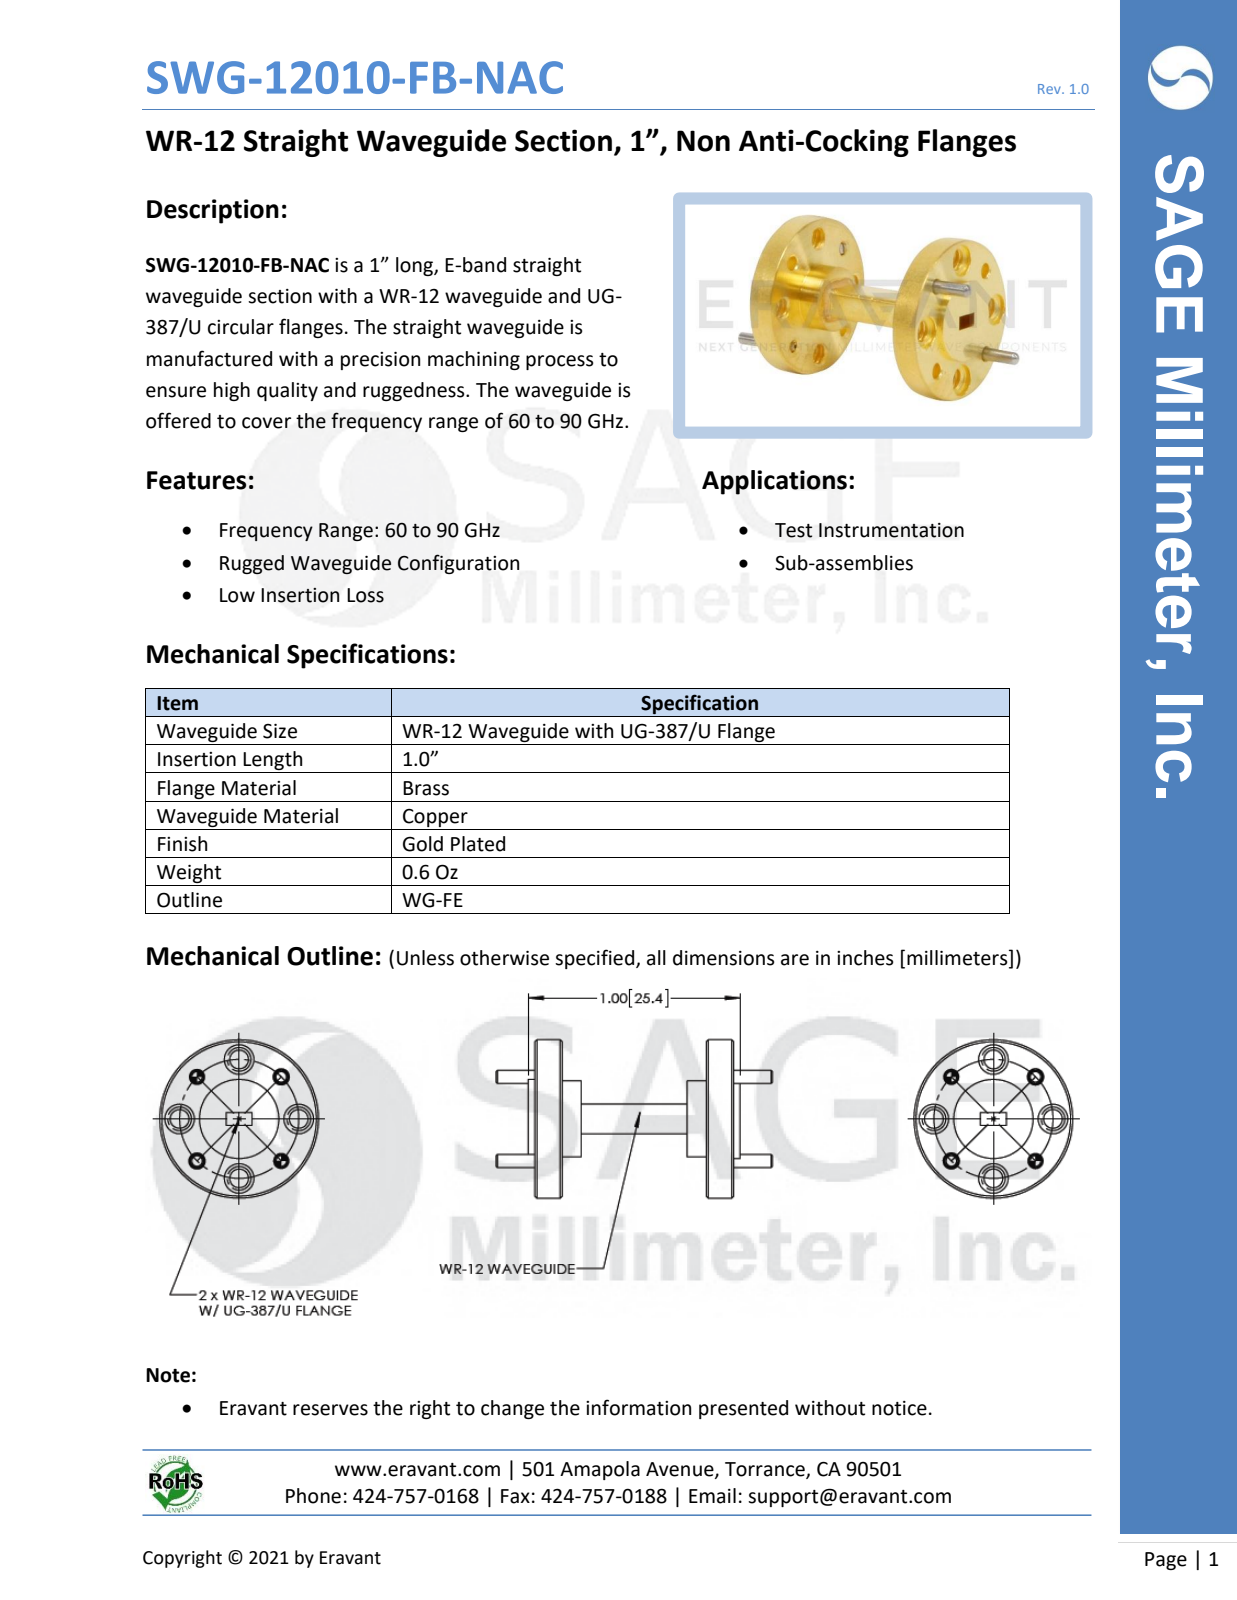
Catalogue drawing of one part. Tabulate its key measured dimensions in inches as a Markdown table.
| quantity | value |
| --- | --- |
| part name | SWG-12010-F1 |
| STEP written by | SolidWorks 2013 (CONFIG_CONTROL_DESIGN) |
| units | inches |
| bodies | 5 solids, 140 faces (32 planar, 68 cylindrical, 40 other) |
| overall size | 1.305 × 0.75 × 0.75 |
| volume | 0.139 in³ |
| surface area | 3.87 in² |
| round holes (diameter × count) | 0.061 × 4, 0.067 × 4, 0.089 × 4, 0.14 × 4 |
| round bosses / shafts (diameter × count) | 0.063 × 4, 0.75 × 1, 0.375 × 1, 0.36 × 1 |
| main face-to-face distances | 0.13, 0.81, 0.68, 0.94, 0.04, 0.04, 0.25, 0.75, 0.061, 0.03 |
| hole center spacings | 0.215, 0.398, 0.519, 0.562, 0.52, 0.563 |
